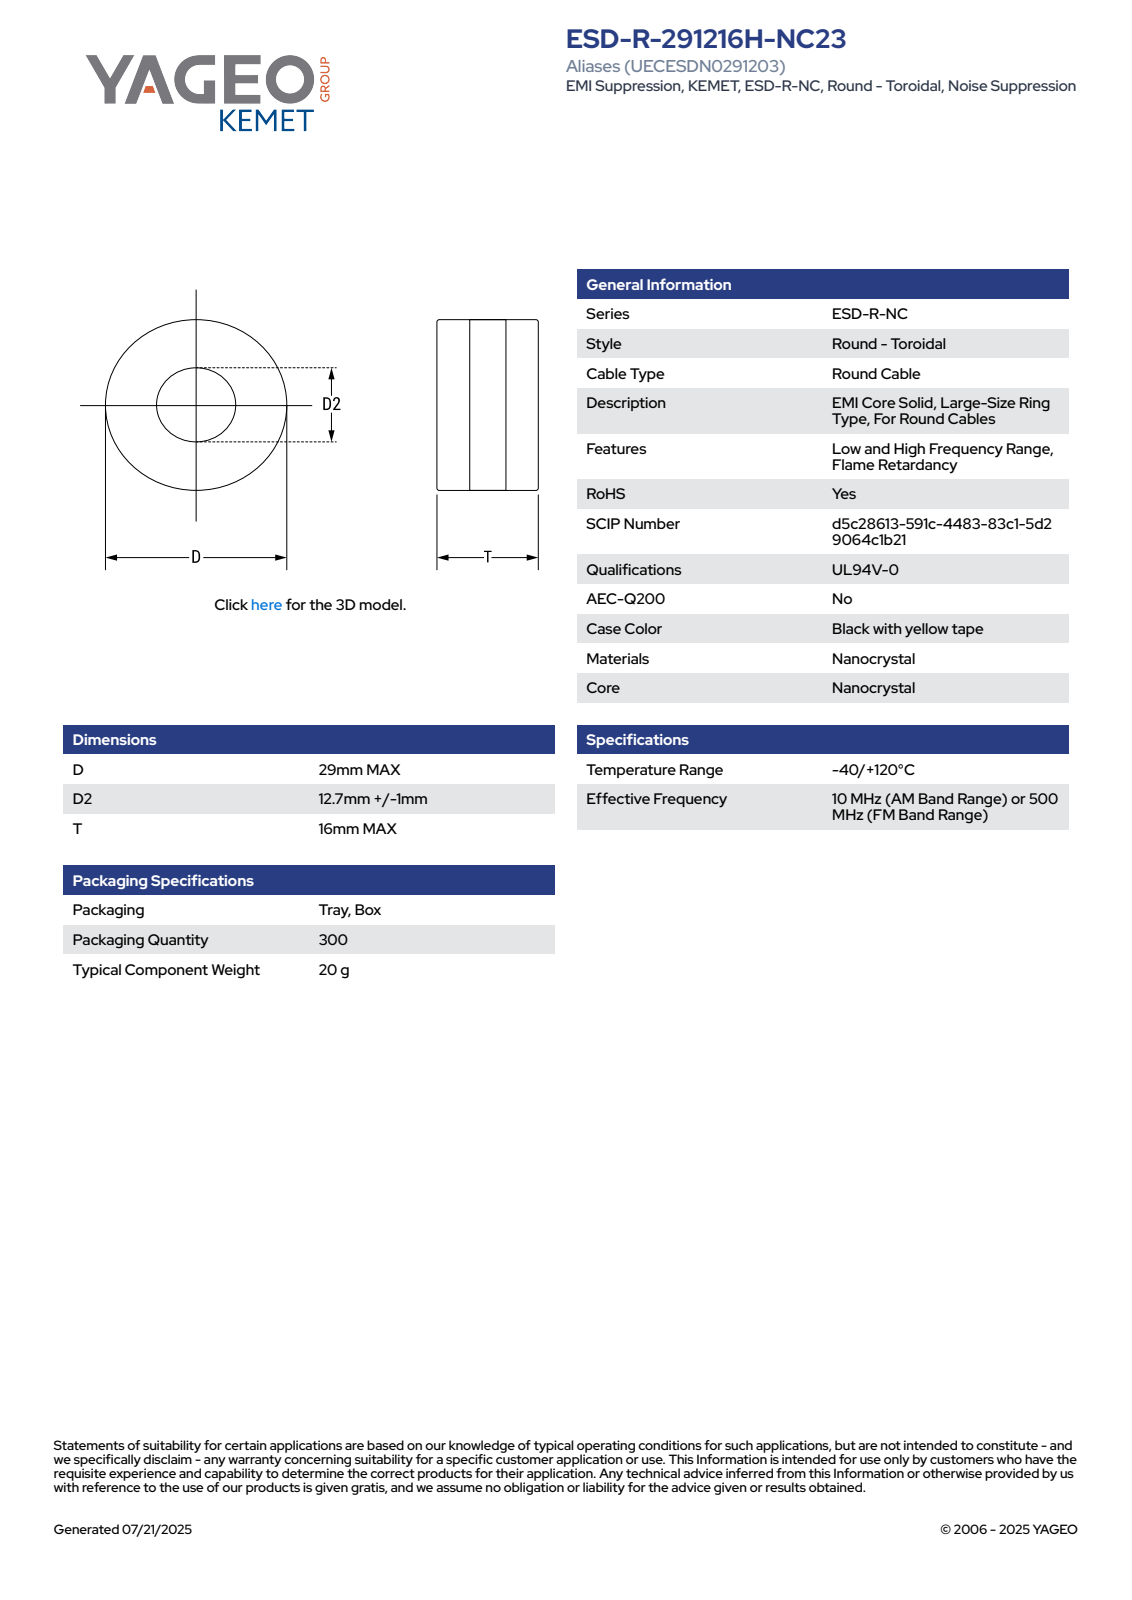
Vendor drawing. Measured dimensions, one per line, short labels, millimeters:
name: EC_ESDRNC23_D29D213.7T16
written by: SolidWorks 2014 (AUTOMOTIVE_DESIGN)
unit: mm
bodies: 1 solid, 74 faces (26 planar, 9 cylindrical, 39 other)
size: 29.03 × 29.02 × 16
volume: 8 188 mm³; area: 3 094 mm²
holes: 1× ⌀13.7
bosses: 1× ⌀29.02, 1× ⌀29
rounds: 1× R14.52
face distances: 16, 5.25, 15.25, 10, 10.75, 0.75, 6.54, 1.29, 8.71, 9.46
